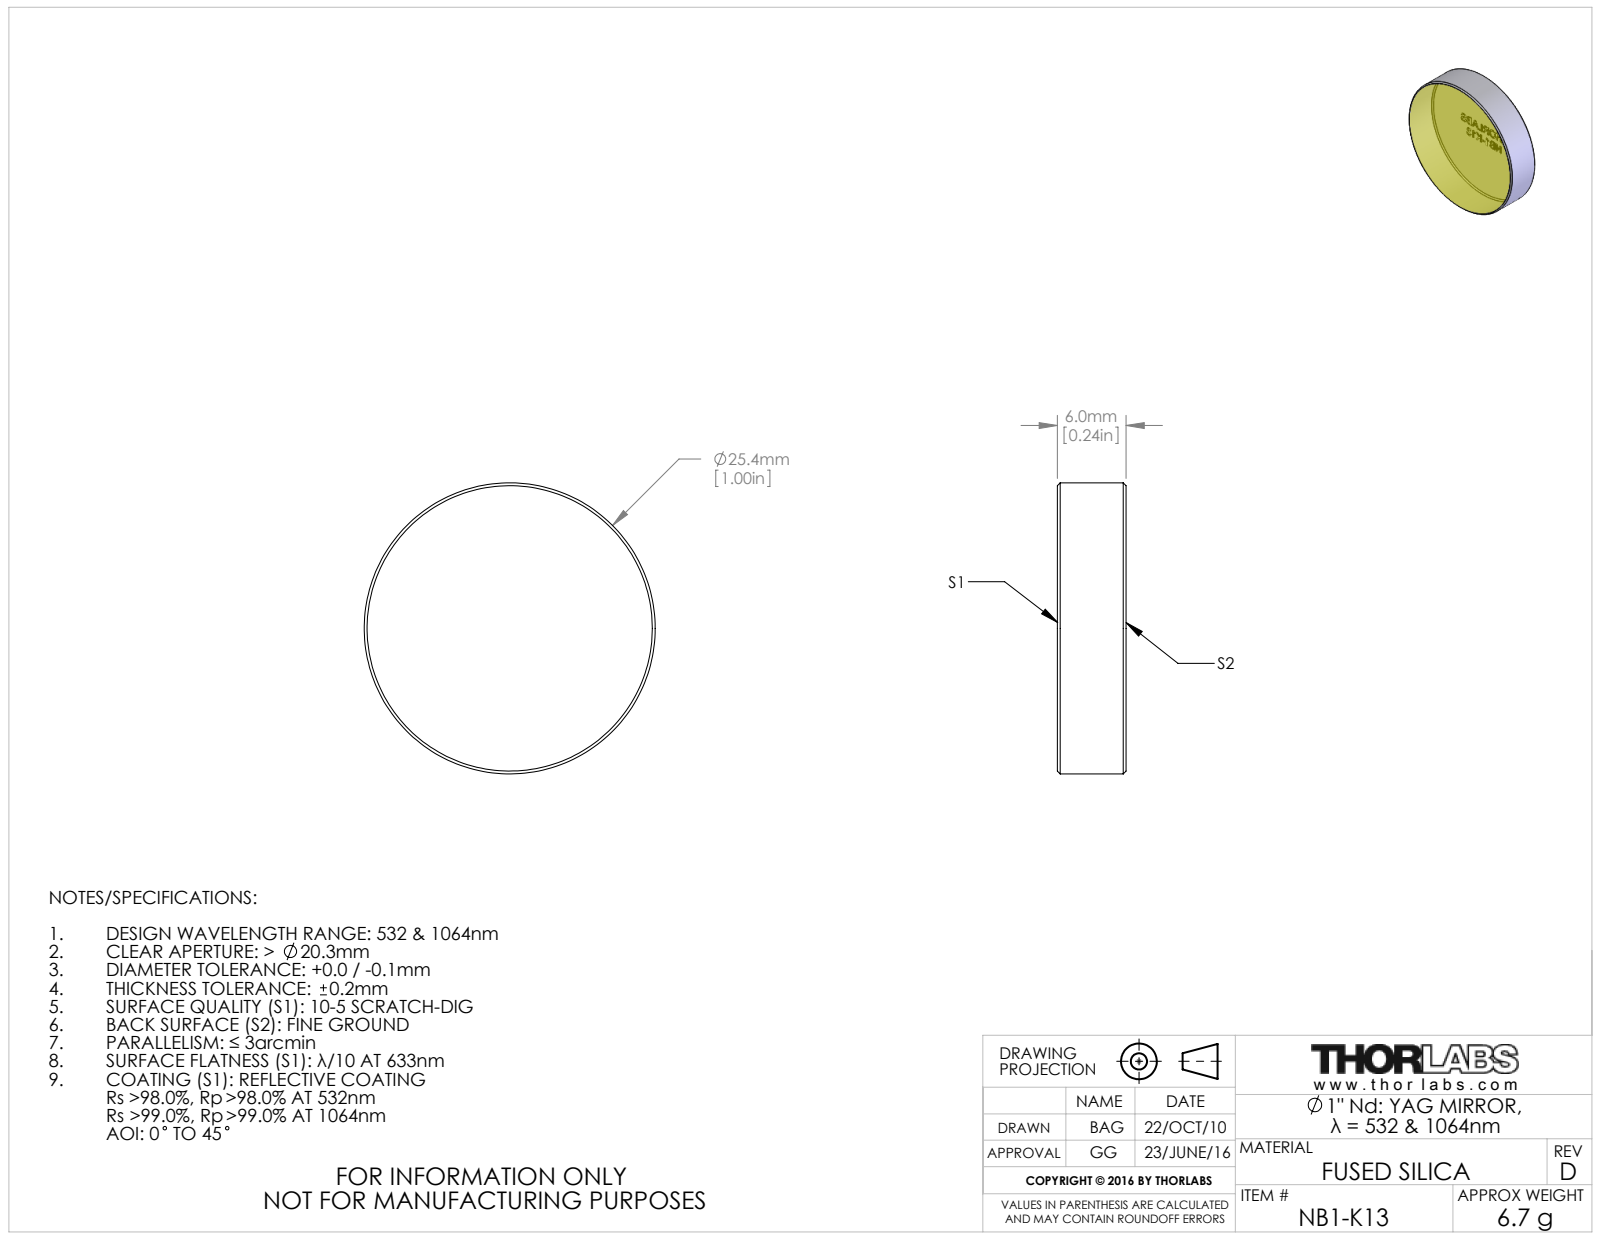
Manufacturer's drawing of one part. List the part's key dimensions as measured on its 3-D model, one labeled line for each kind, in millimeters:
Part name (STEP PRODUCT): 19191-E0W
STEP written by: SolidWorks 2016 (CONFIG_CONTROL_DESIGN)
Units: millimetres
Bodies: 1 solid, 207 faces (131 planar, 2 cylindrical, 74 other)
Overall size (bounding box): 25.4 × 25.4 × 6
Volume: 3 030 mm³ · Surface area: 1 468 mm²
Round bosses / shafts (diameter × count): ⌀25.4 ×1
Main face-to-face distances: 6, 1.5, 2.4, 2.4, 3.3, 1.9, 4.1, 1.8, 2.2, 1.4
